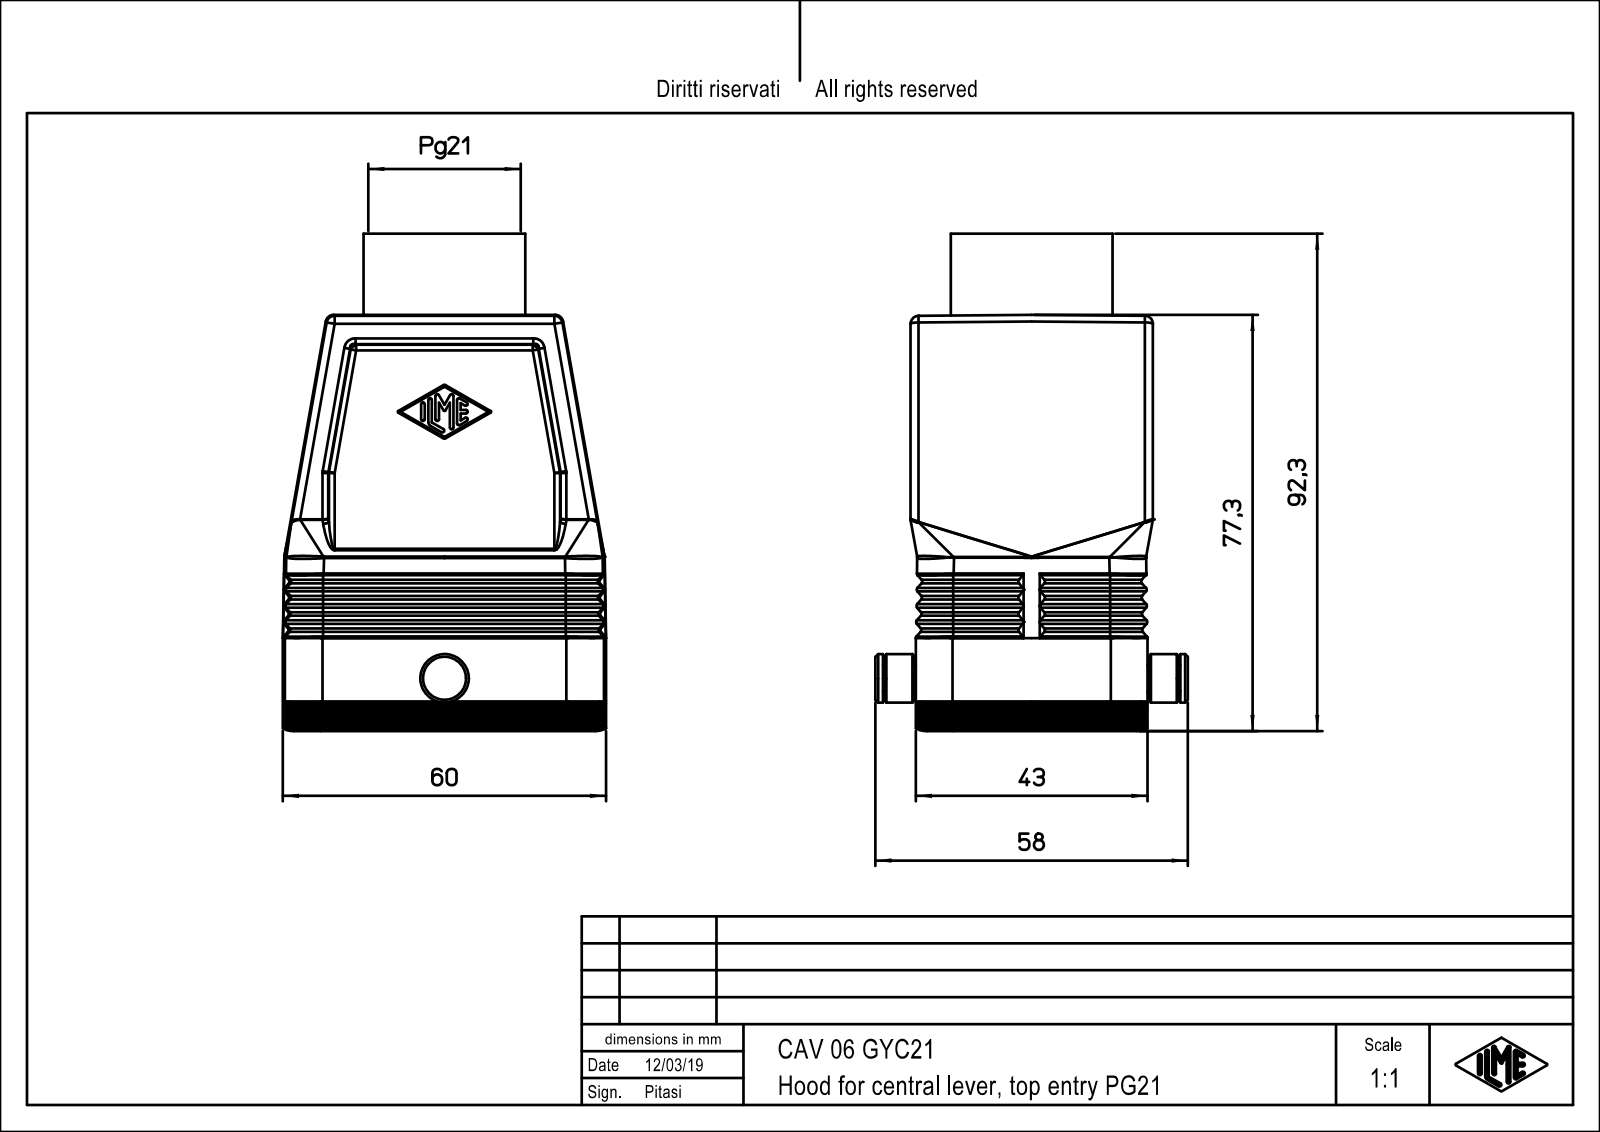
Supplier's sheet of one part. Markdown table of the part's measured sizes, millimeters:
| quantity | value |
| --- | --- |
| part name | CAV_06_GYC21 |
| STEP written by | PTC Creo Elements/Direct Modeling 19.0E 27-Jun-2016 (C) Parametric Technology GmbH (AUTOMOTIVE_DESIGN) |
| units | millimeters |
| bodies | 1 solid, 530 faces (174 planar, 176 cylindrical, 180 other) |
| overall size | 92.25 × 60 × 58 |
| volume | 67 631 mm³ |
| surface area | 35 246 mm² |
| round holes (diameter × count) | 3 × 4, 24 × 1, 27.54 × 1 |
| round bosses / shafts (diameter × count) | 30 × 1, 28.3 × 1, 9 × 1, 4.8 × 1 |
| partial cylindrical surfaces (radius × count) | 0.5 × 54, 1.5 × 44, 3 × 12, 7 × 12, 4 × 4, 4.2 × 4, 5.8 × 4 |
| main face-to-face distances | 43, 4, 7, 2, 1, 7.55, 44, 60, 39, 66.05 |
| hole center spacings | 25.81, 27, 44, 51.62 |
